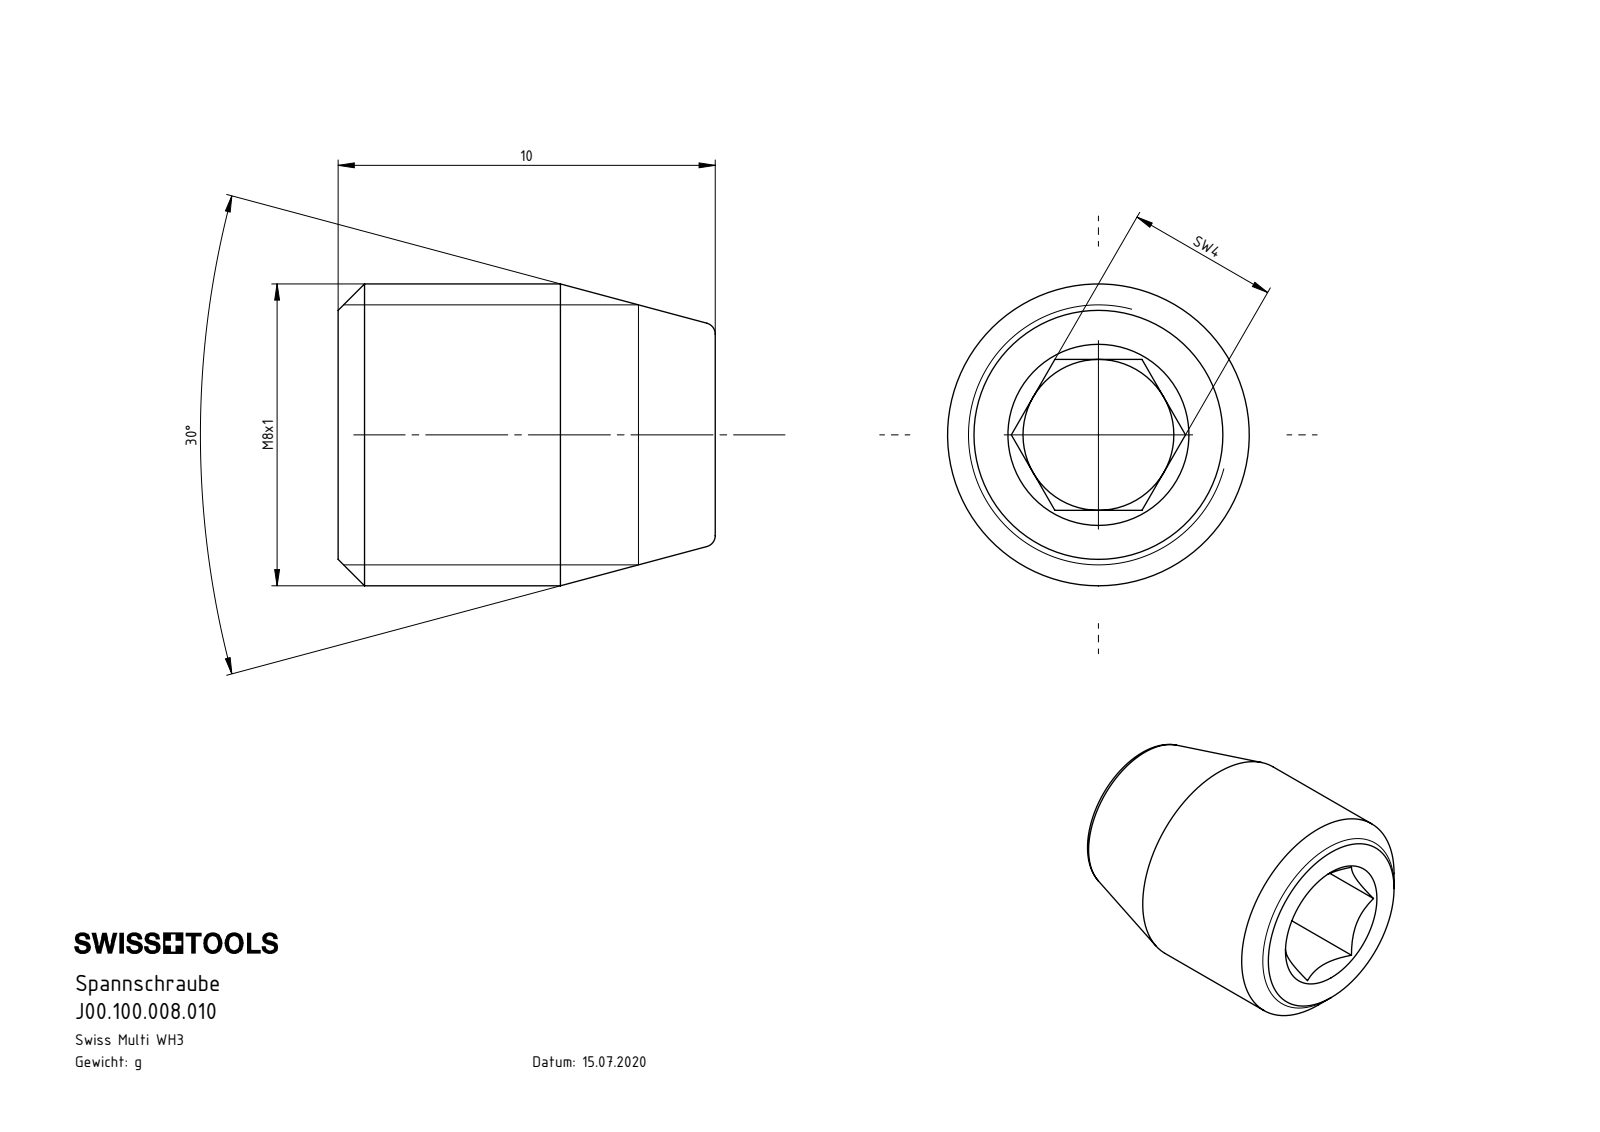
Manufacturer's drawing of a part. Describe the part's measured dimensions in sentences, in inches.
The part is named "WH3.ER1.001.010". Its 3-D file was written by "SolidWorks 2017 (AUTOMOTIVE_DESIGN)". It is 1 solid with 21 faces: 14 planar, 2 cylindrical and 5 other. Overall it measures 0.394 by 0.315 by 0.315 inches. Its volume is 0.022 cubic inches and its surface area 0.597 square inches. Round holes: 1 of diameter 0.157. Round bosses or shafts: 1 of diameter 0.315. The main face-to-face distances are 0.157, 0.394, 0.197.
